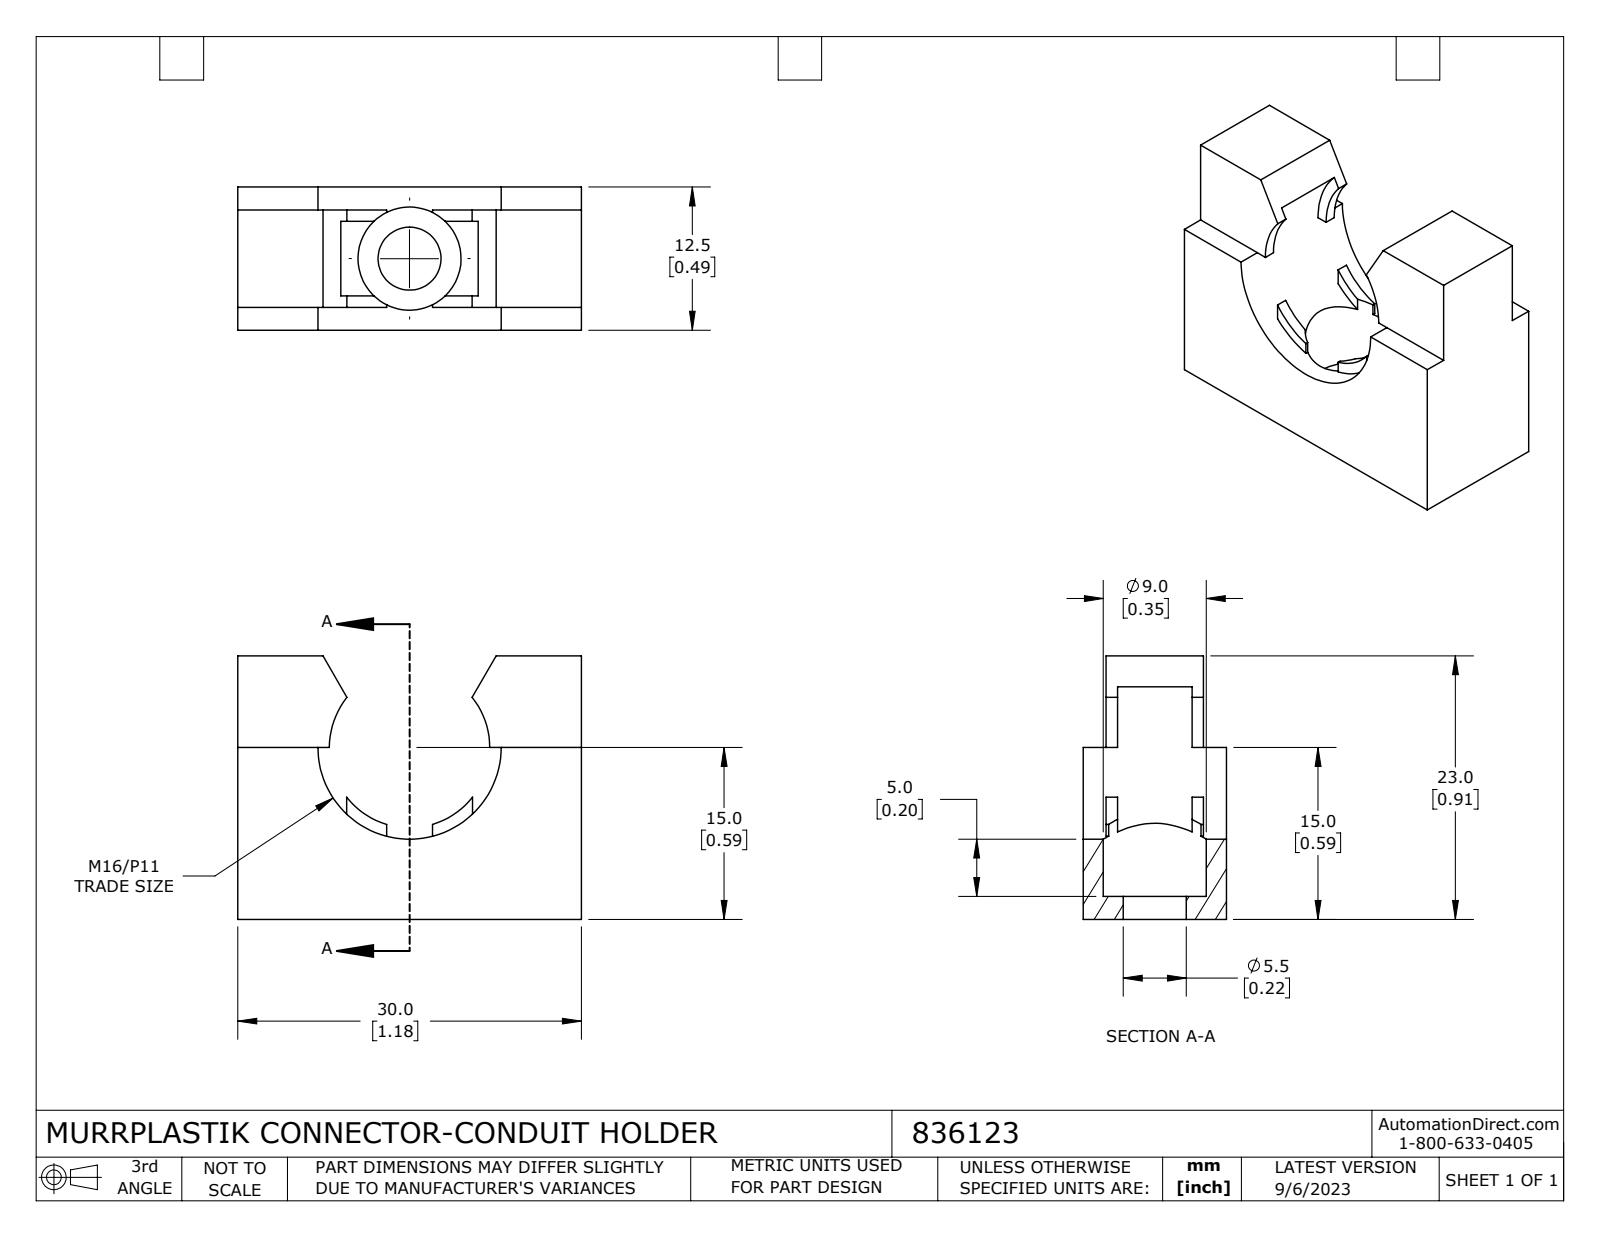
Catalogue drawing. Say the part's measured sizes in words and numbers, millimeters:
The part is named "836123". Its 3-D file was written by "SolidWorks 2021 (CONFIG_CONTROL_DESIGN)". It is 1 solid with 57 faces: 42 planar, 15 cylindrical and 0 other. Overall it measures 30 by 23 by 12.5 millimeters. Its volume is 5 080 cubic millimeters and its surface area 2 717 square millimeters. Round holes: 1 of diameter 5.5, 1 of diameter 9. Partial cylindrical surfaces (rounded edges, fillets, slot ends): 1 of radius 7, 1 of radius 8. The main face-to-face distances are 12.5, 2, 10.5, 30, 8.5, 23, 15, 8, 13, 21.
